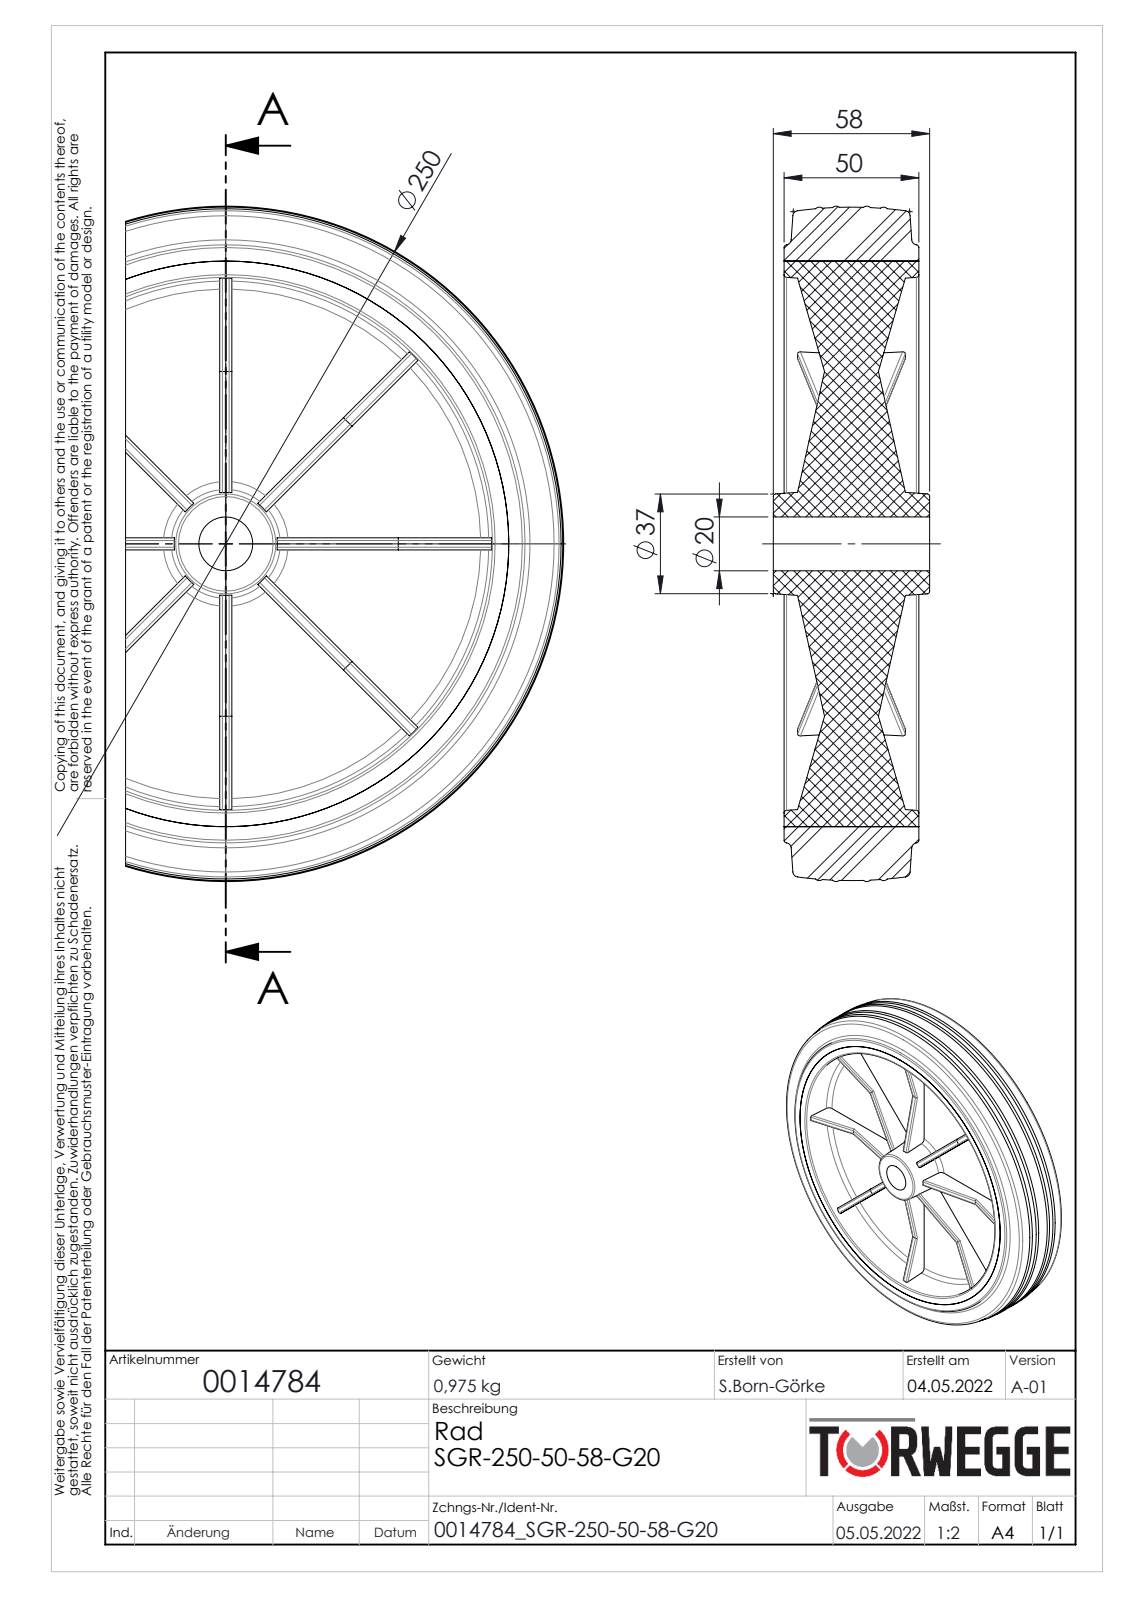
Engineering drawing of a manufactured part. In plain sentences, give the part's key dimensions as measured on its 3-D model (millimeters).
The part is named "0014784". Its 3-D file was written by "SolidWorks 2020 (AUTOMOTIVE_DESIGN)". It is 2 solids with 246 faces: 86 planar, 70 cylindrical and 90 other. Overall it measures 250.78 by 250.78 by 58 millimeters. Its volume is 1 104 000 cubic millimeters and its surface area 260 242 square millimeters. Round holes: 1 of diameter 20, 1 of diameter 210. Partial cylindrical surfaces (rounded edges, fillets, slot ends): 64 of radius 1. The main face-to-face distances are 4, 4.5, 27, 23, 50, 31, 54, 58, 47.4, 47.39.
